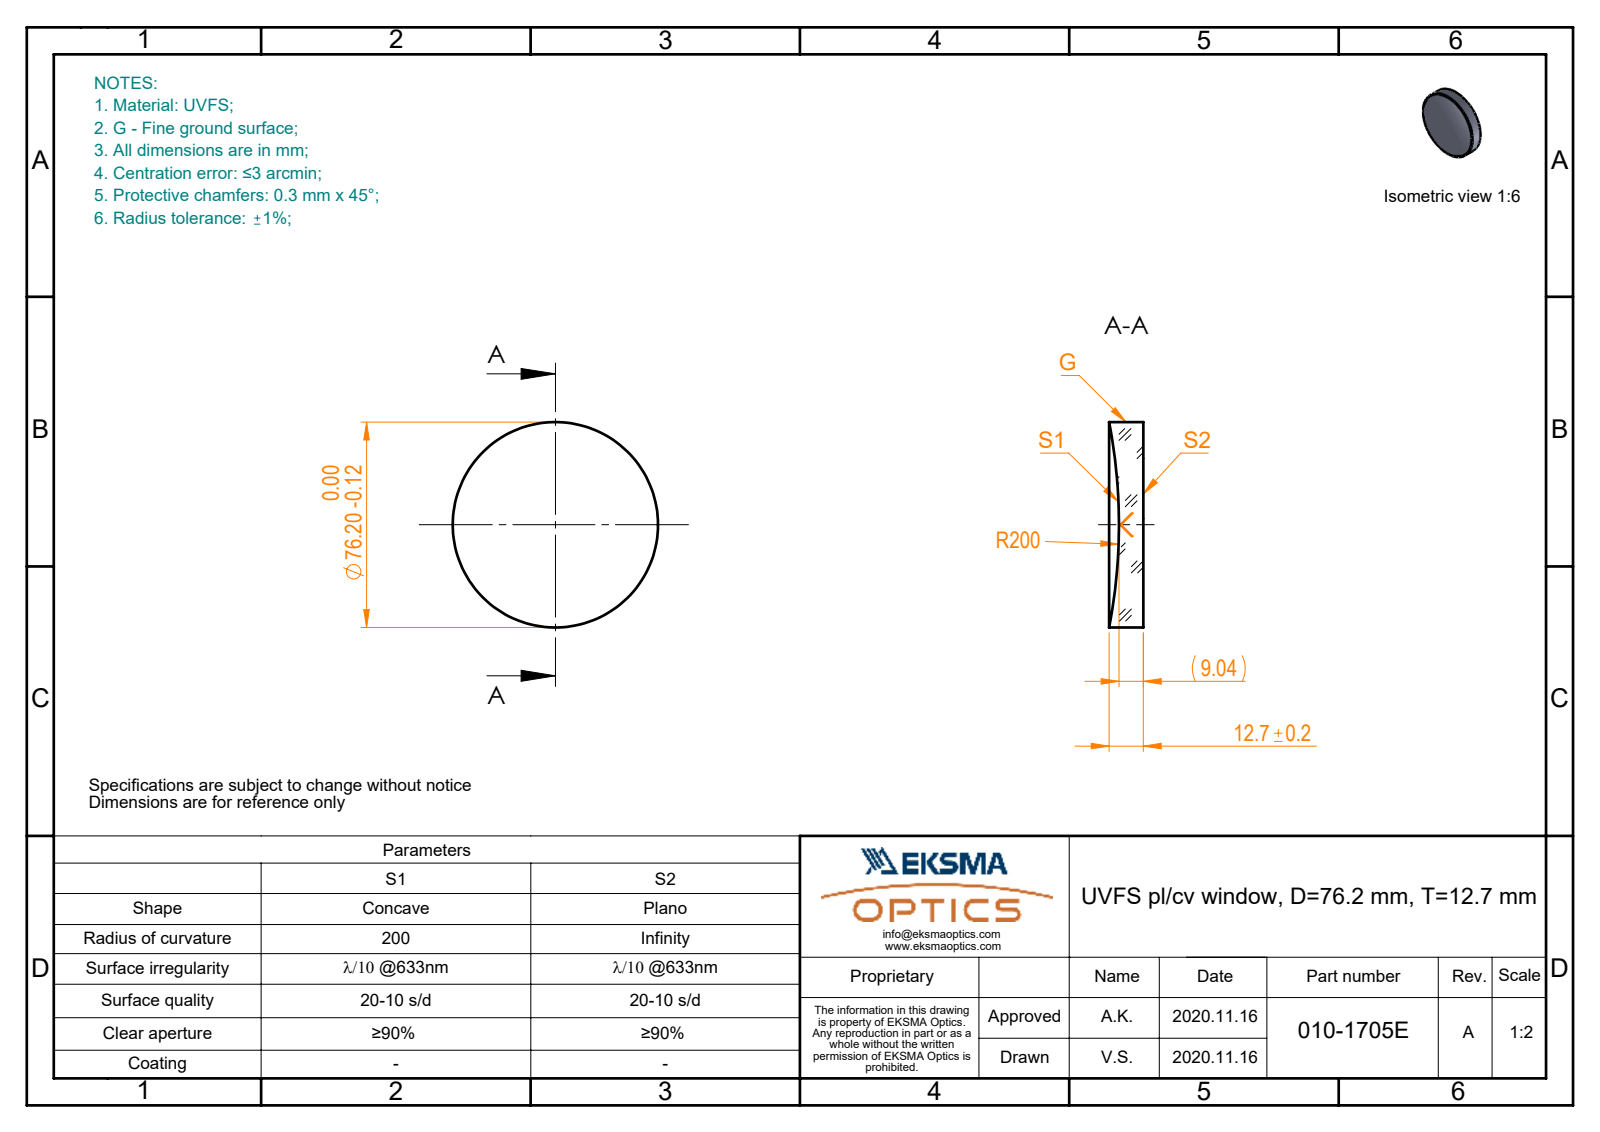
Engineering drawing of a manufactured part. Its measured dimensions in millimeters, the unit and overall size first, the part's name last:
Units: millimetres
Overall size (bounding box): 76.2 × 76.2 × 12.7
Round bosses / shafts (diameter × count): ⌀76.2 ×1
Volume: 49 540 mm³ · Surface area: 12 203 mm²
Bodies: 1 solid, 5 faces (1 planar, 2 cylindrical, 2 other)
Part name (STEP PRODUCT): 010-1705E_UVFS_PCV_window
STEP written by: SolidWorks 2019 (CONFIG_CONTROL_DESIGN)
